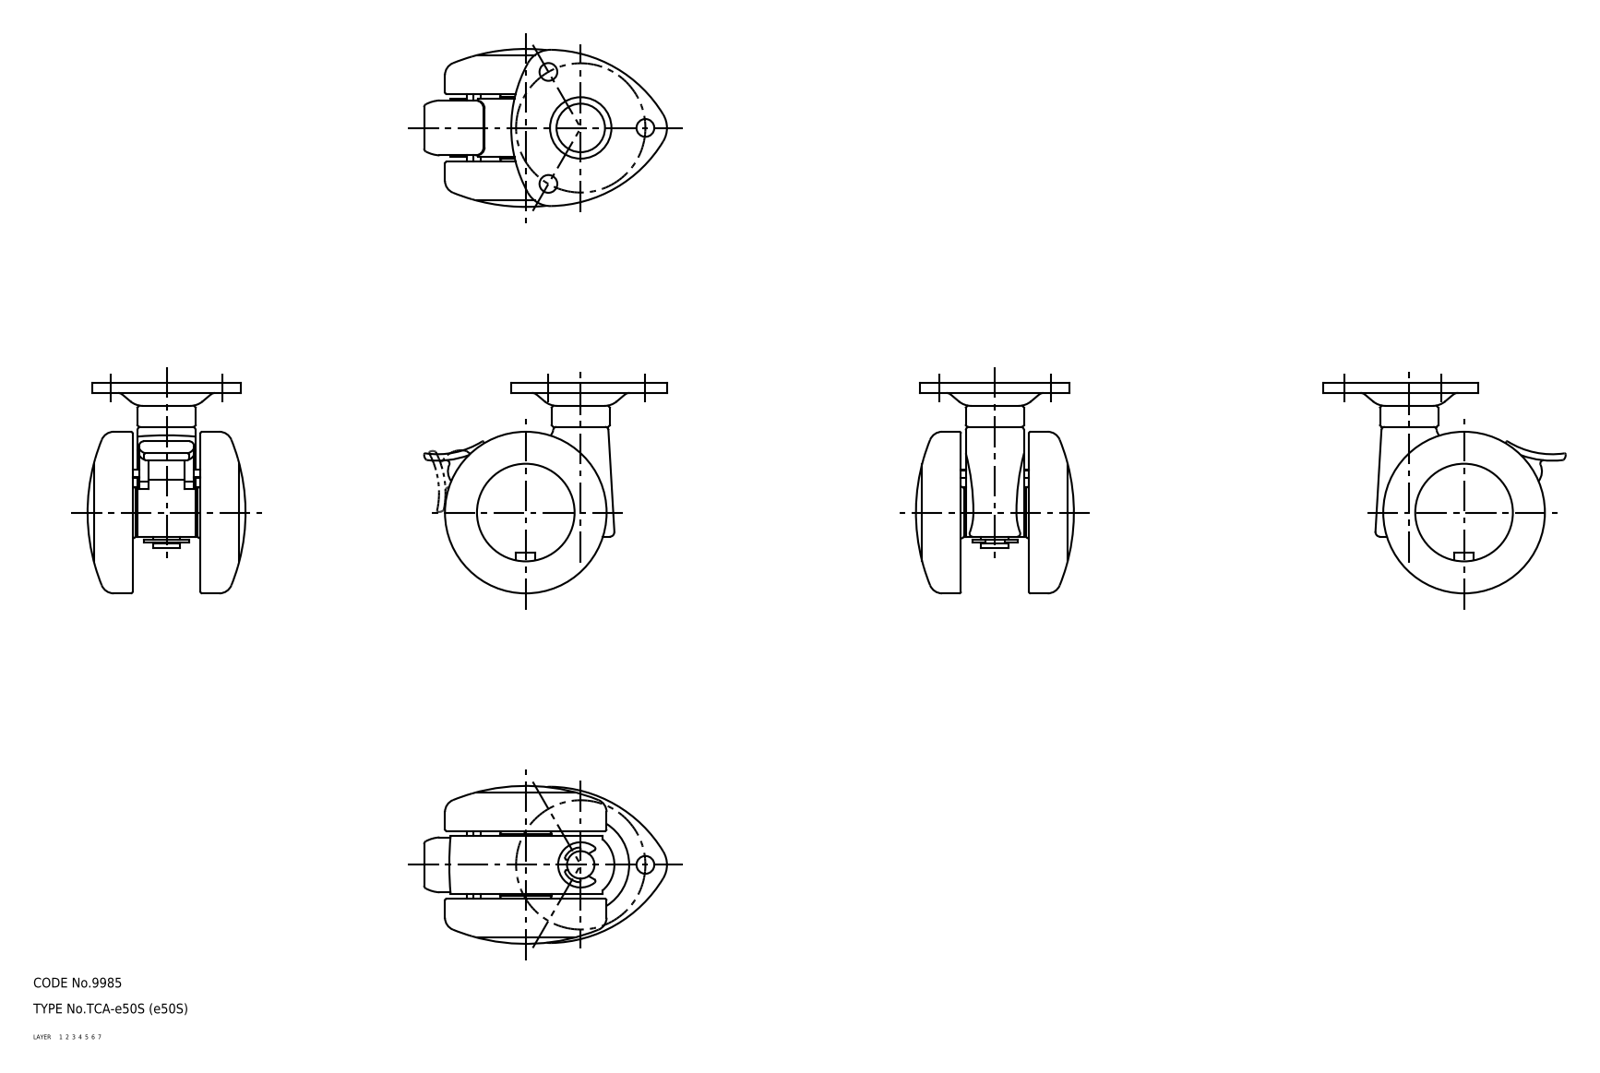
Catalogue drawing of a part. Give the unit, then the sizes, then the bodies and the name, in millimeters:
Units: millimetres
Overall size (bounding box): 75.11 × 65 × 48.86
Volume: 67 493 mm³ · Surface area: 31 163 mm²
Bodies: 6 solids, 242 faces (0 planar, 0 cylindrical, 242 other)
Part name (STEP PRODUCT): lever; wheel_mr; wheel; mounting plate (+2 more)
STEP written by: CADfix (AUTOMOTIVE_DESIGN)
